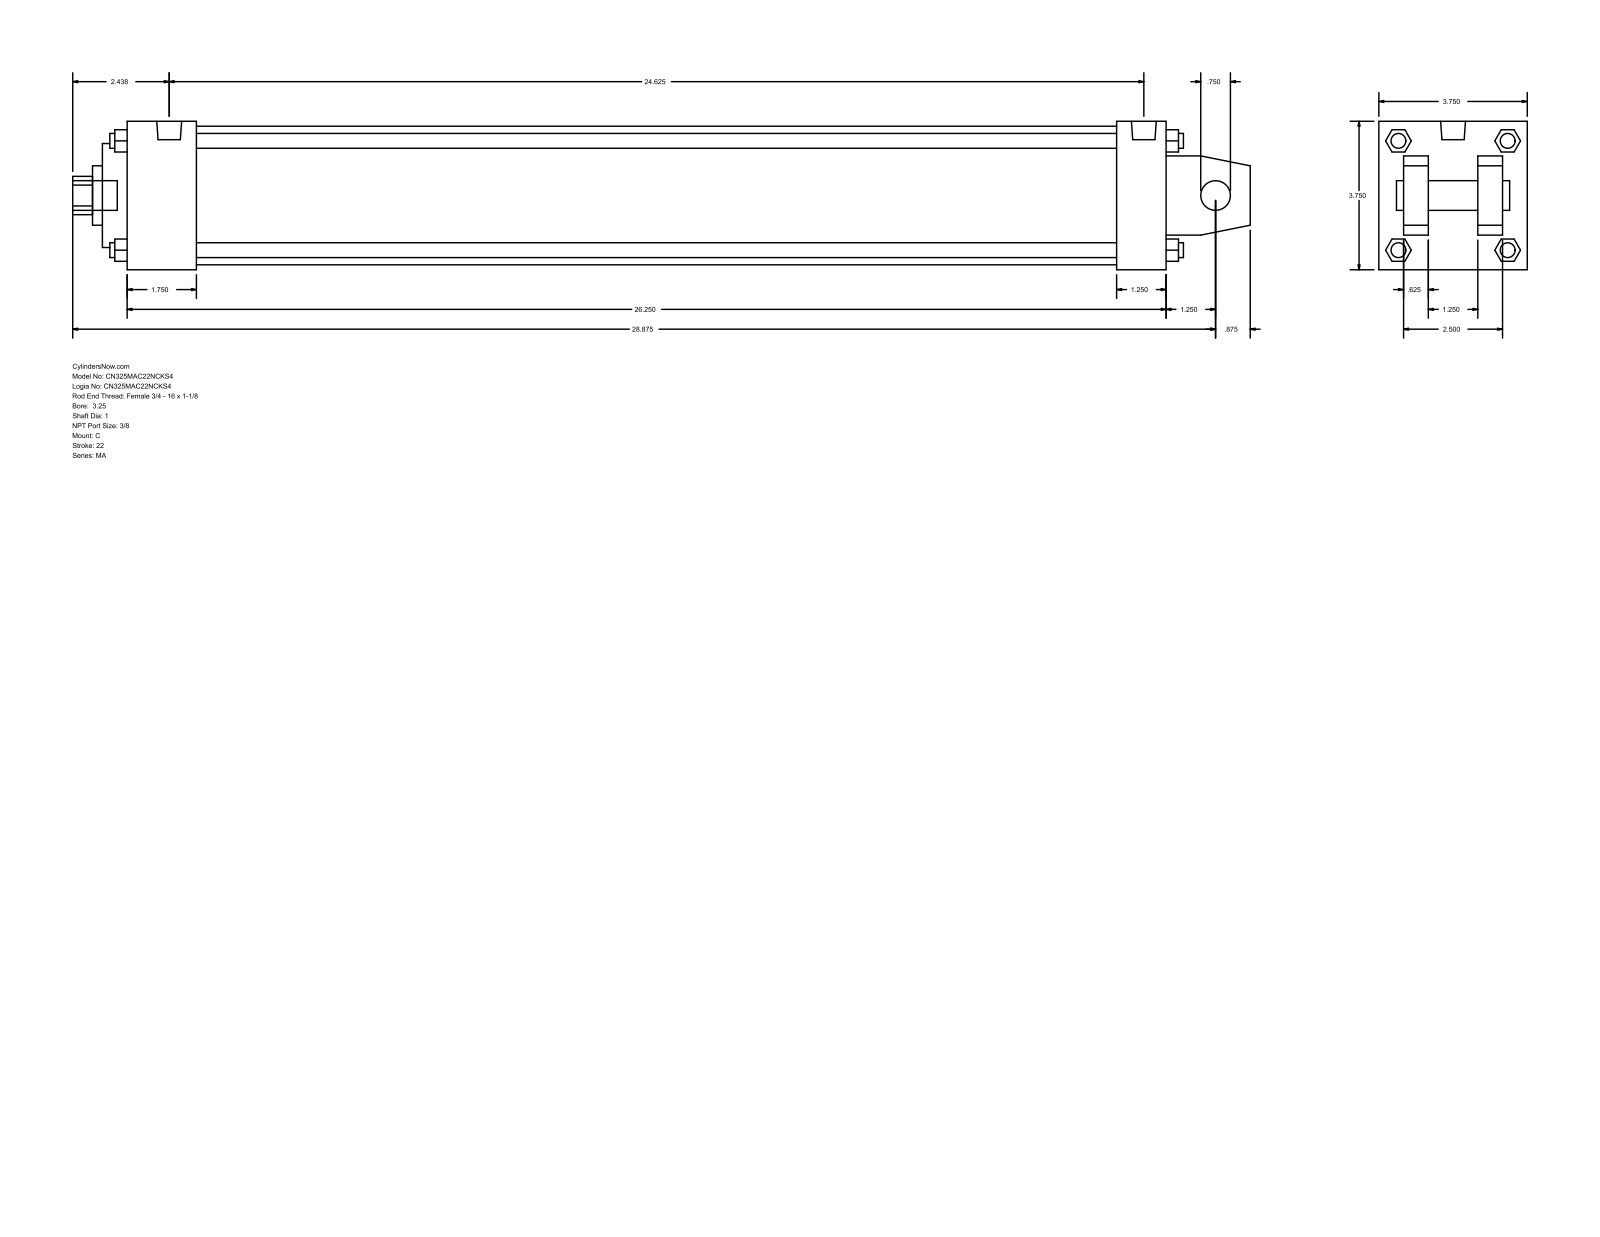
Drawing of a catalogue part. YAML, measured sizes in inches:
part_name: "MA_C__0325_1"
step_written_by: "GSSL Pune (CONFIG_CONTROL_DESIGN)"
units: inches
bodies: {solids: 0, faces: 141, planar: 109, cylindrical: 32, other: 0}
overall_size: [29.75, 3.75, 3.75]
round_holes:
  - {diameter: 0.75, count: 1}
  - {diameter: 1, count: 1}
  - {diameter: 1.5, count: 1}
  - {diameter: 2.625, count: 1}
  - {diameter: 3.5, count: 1}
round_bosses_or_shafts:
  - {diameter: 0.437, count: 4}
  - {diameter: 0.375, count: 4}
  - {diameter: 0.627, count: 2}
  - {diameter: 0.75, count: 1}
partial_cylinders:
  - {radius: 0.484, count: 1}
face_to_face_distances: [3.75, 0.625, 2.5, 26.25, 1.25, 3.125, 1.875, 26.875, 25, 1.25]
